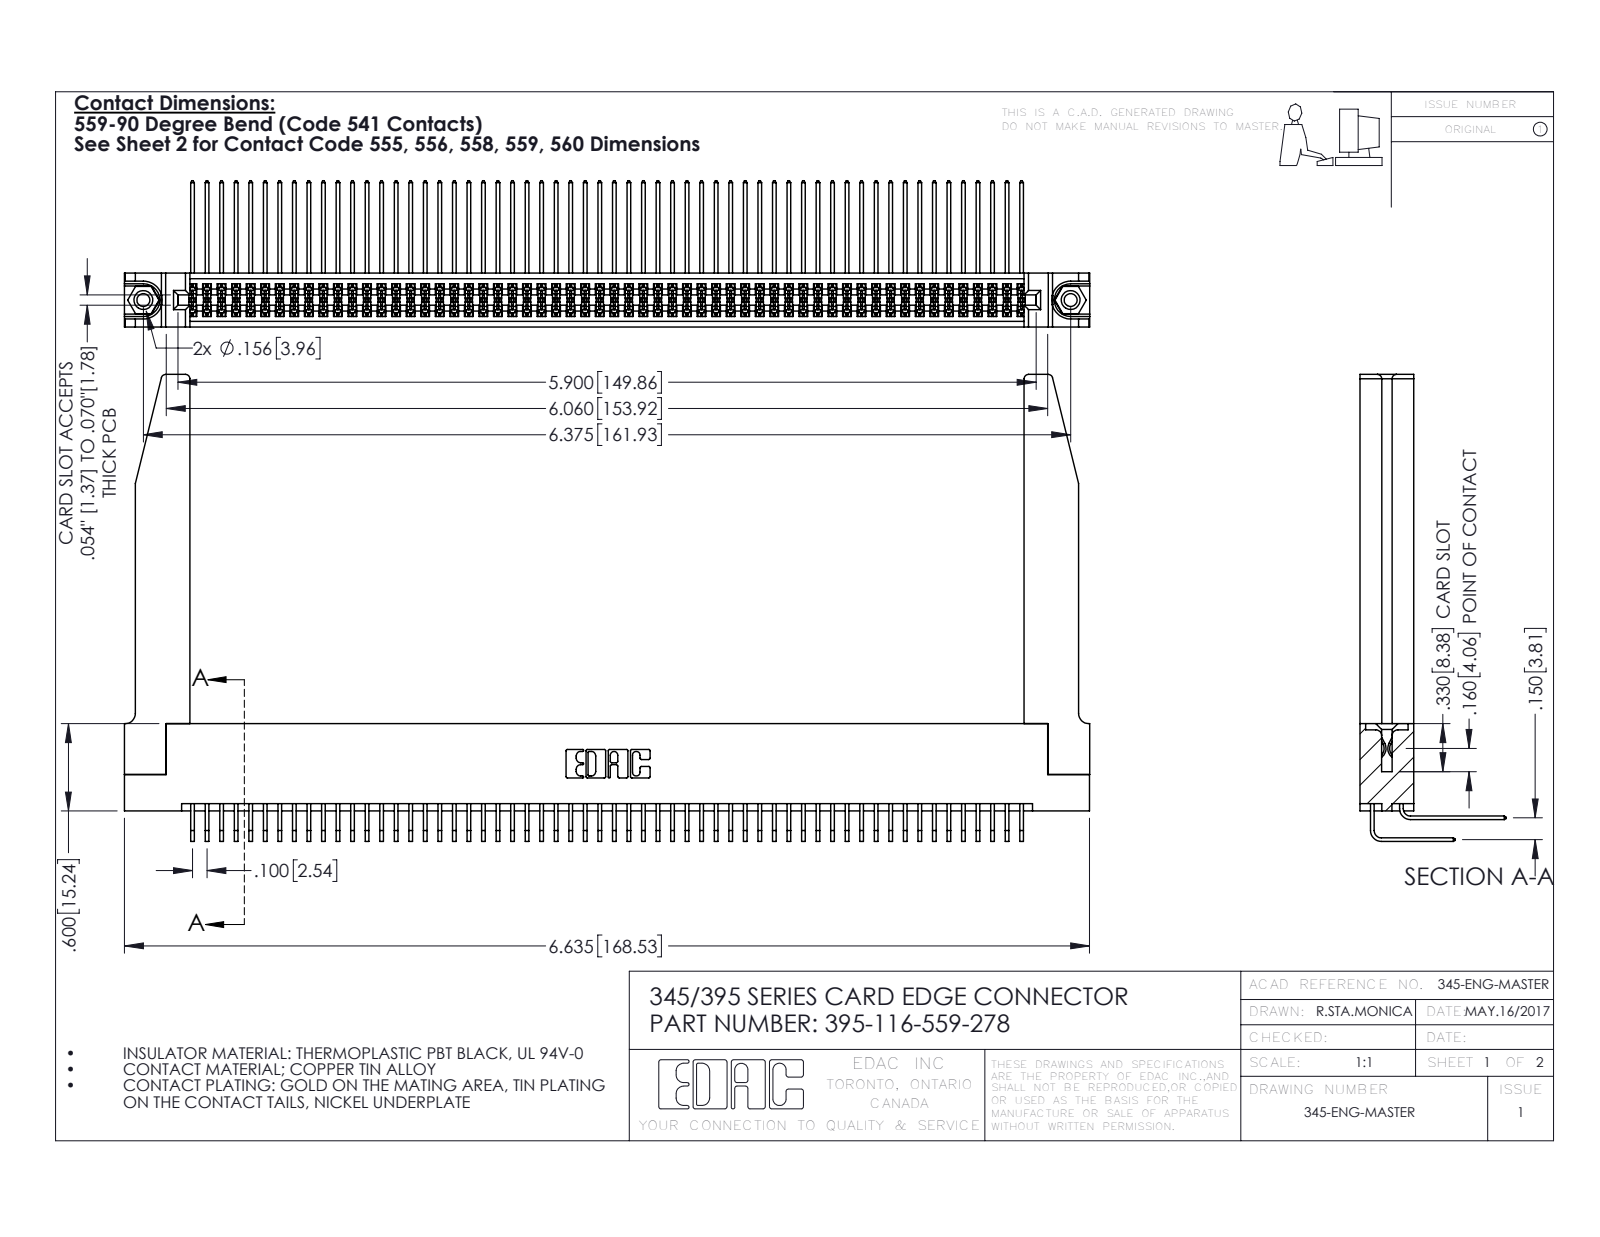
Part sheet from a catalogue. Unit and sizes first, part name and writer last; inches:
Units: inches
Overall size (bounding box): 6.636 × 3.209 × 1.005
Round holes (diameter × count): ⌀0.089 ×2, ⌀0.125 ×2, ⌀0.156 ×2, ⌀0.064 ×1
Round bosses / shafts (diameter × count): ⌀0.155 ×2
Partial cylindrical surfaces — rounded edges, fillets, slot ends (radius × count): R0.006 ×174, R0.01 ×22, R0.03 ×8, R0.007 ×6, R0.031 ×6, R0.026 ×3, R0.014 ×2, R0.019 ×2
Main face-to-face distances: 0.072, 0.298, 0.37, 0.2, 0.098, 0.272, 0.025, 0.225, 0.175, 0.15
Hole centre spacings: 0.27, 6.139, 6.375
Volume: 1.523 in³ · Surface area: 55.35 in²
Bodies: 121 solids, 6392 faces (4282 planar, 2058 cylindrical, 52 other)
Part name (STEP PRODUCT): 345-250-001_345-250-001-102; 395-116-559-278; 345-220-078_345-220-078; 345-292-001_558 559 Tail - 1 (+2 more)
STEP written by: SolidWorks 2016 (CONFIG_CONTROL_DESIGN)
